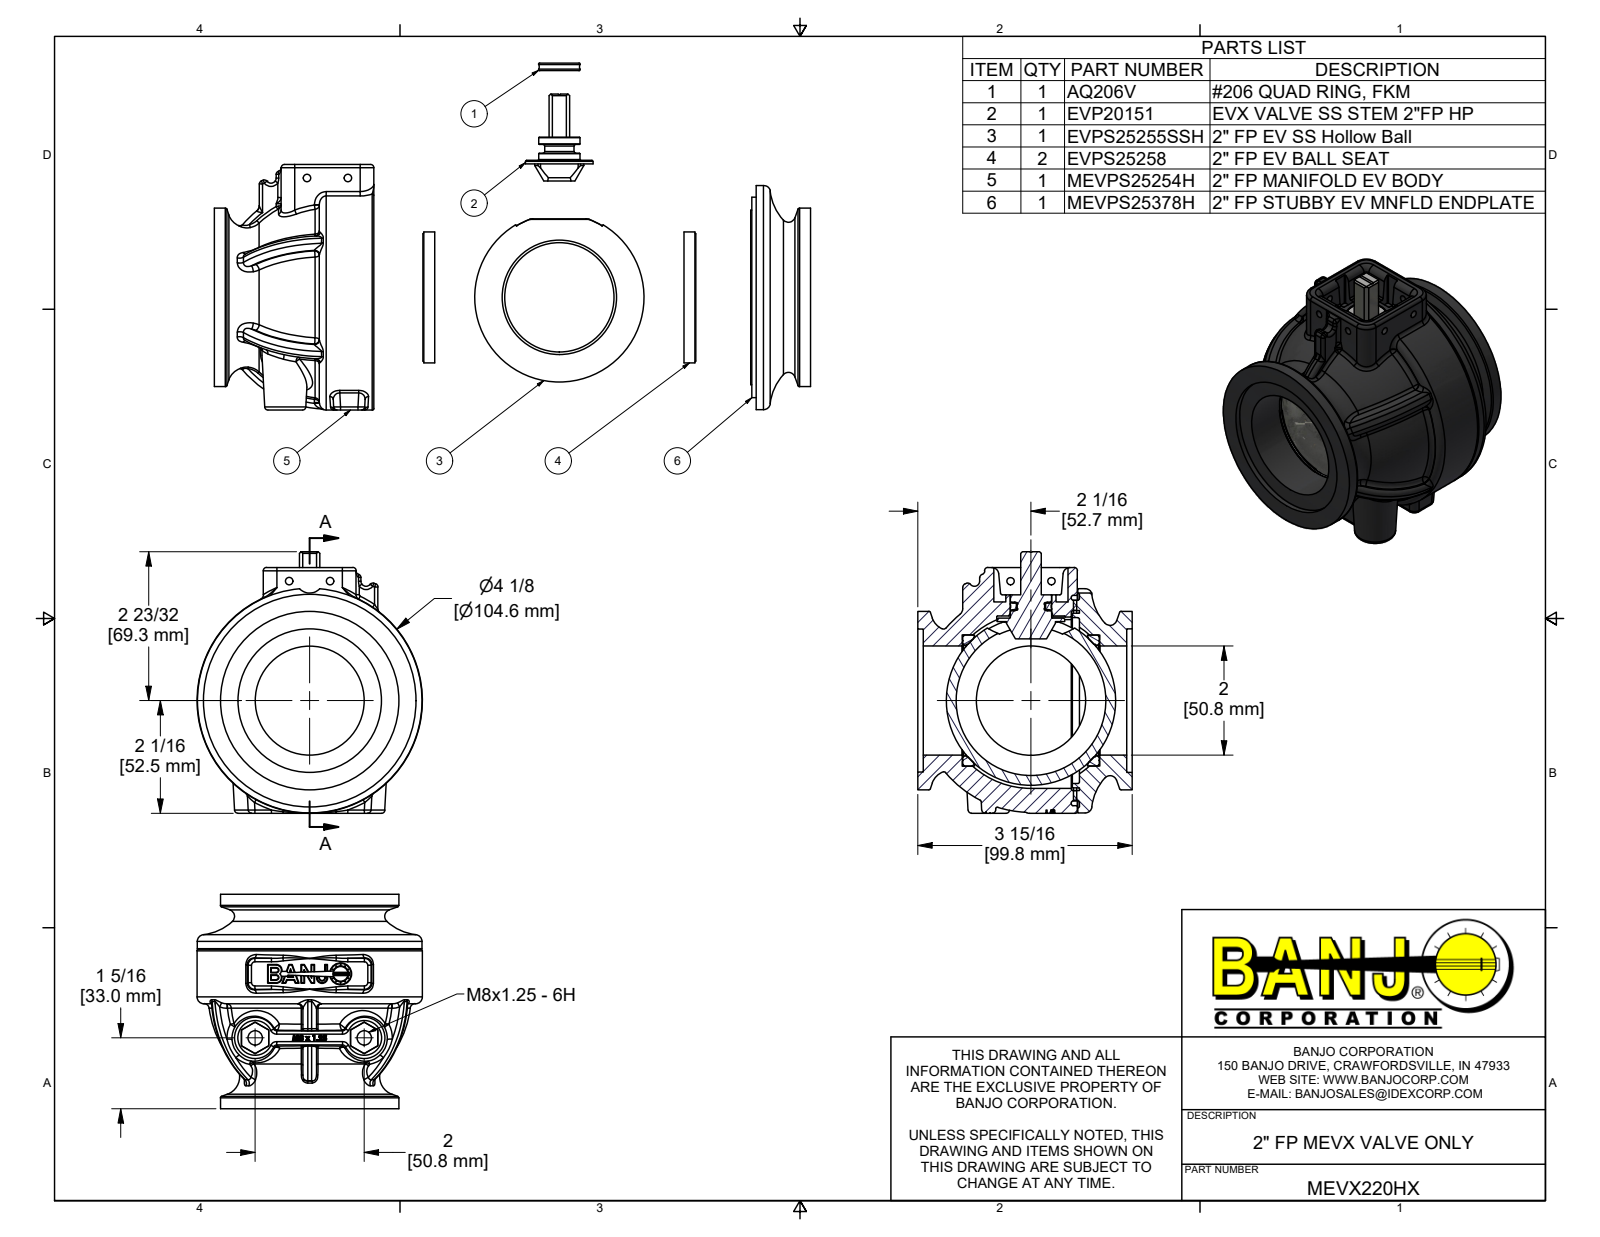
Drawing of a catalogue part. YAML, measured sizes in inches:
part_name: "MEVX220HX; AQ206V; EVP20151; EVPS25255SSH (+5 more)"
step_written_by: "Autodesk Inventor 2022 (AUTOMOTIVE_DESIGN)"
units: inches
bodies: {solids: 9, faces: 1020, planar: 445, cylindrical: 199, other: 376}
overall_size: [4.791, 4.13, 3.93]
volume: 21.8
surface_area: 198.4
round_holes:
  - {diameter: 0.135, count: 4}
  - {diameter: 0.262, count: 2}
  - {diameter: 0.433, count: 2}
  - {diameter: 2, count: 2}
  - {diameter: 0.405, count: 1}
  - {diameter: 0.76, count: 1}
  - {diameter: 1.255, count: 1}
  - {diameter: 2.025, count: 1}
  - {diameter: 2.06, count: 1}
  - {diameter: 2.405, count: 1}
  - {diameter: 2.62, count: 1}
  - {diameter: 2.63, count: 1}
round_bosses_or_shafts:
  - {diameter: 4.13, count: 1}
  - {diameter: 4.117, count: 1}
  - {diameter: 3.675, count: 1}
  - {diameter: 3.27, count: 1}
  - {diameter: 3.2, count: 1}
  - {diameter: 2.401, count: 1}
  - {diameter: 1.24, count: 1}
  - {diameter: 0.755, count: 1}
partial_cylinders:
  - {radius: 0.06, count: 31}
  - {radius: 0.015, count: 20}
  - {radius: 0.09, count: 13}
  - {radius: 0.125, count: 9}
  - {radius: 0.03, count: 8}
  - {radius: 0.059, count: 6}
  - {radius: 0.062, count: 6}
  - {radius: 0.25, count: 5}
face_to_face_distances: [0.1, 3.83, 3.93, 0.965, 1.015, 0.5, 2.965, 2.111, 2.101, 0.411]
hole_center_spacings: [2.219, 0.75, 1.265, 0.693, 1.25, 1.957, 2]
